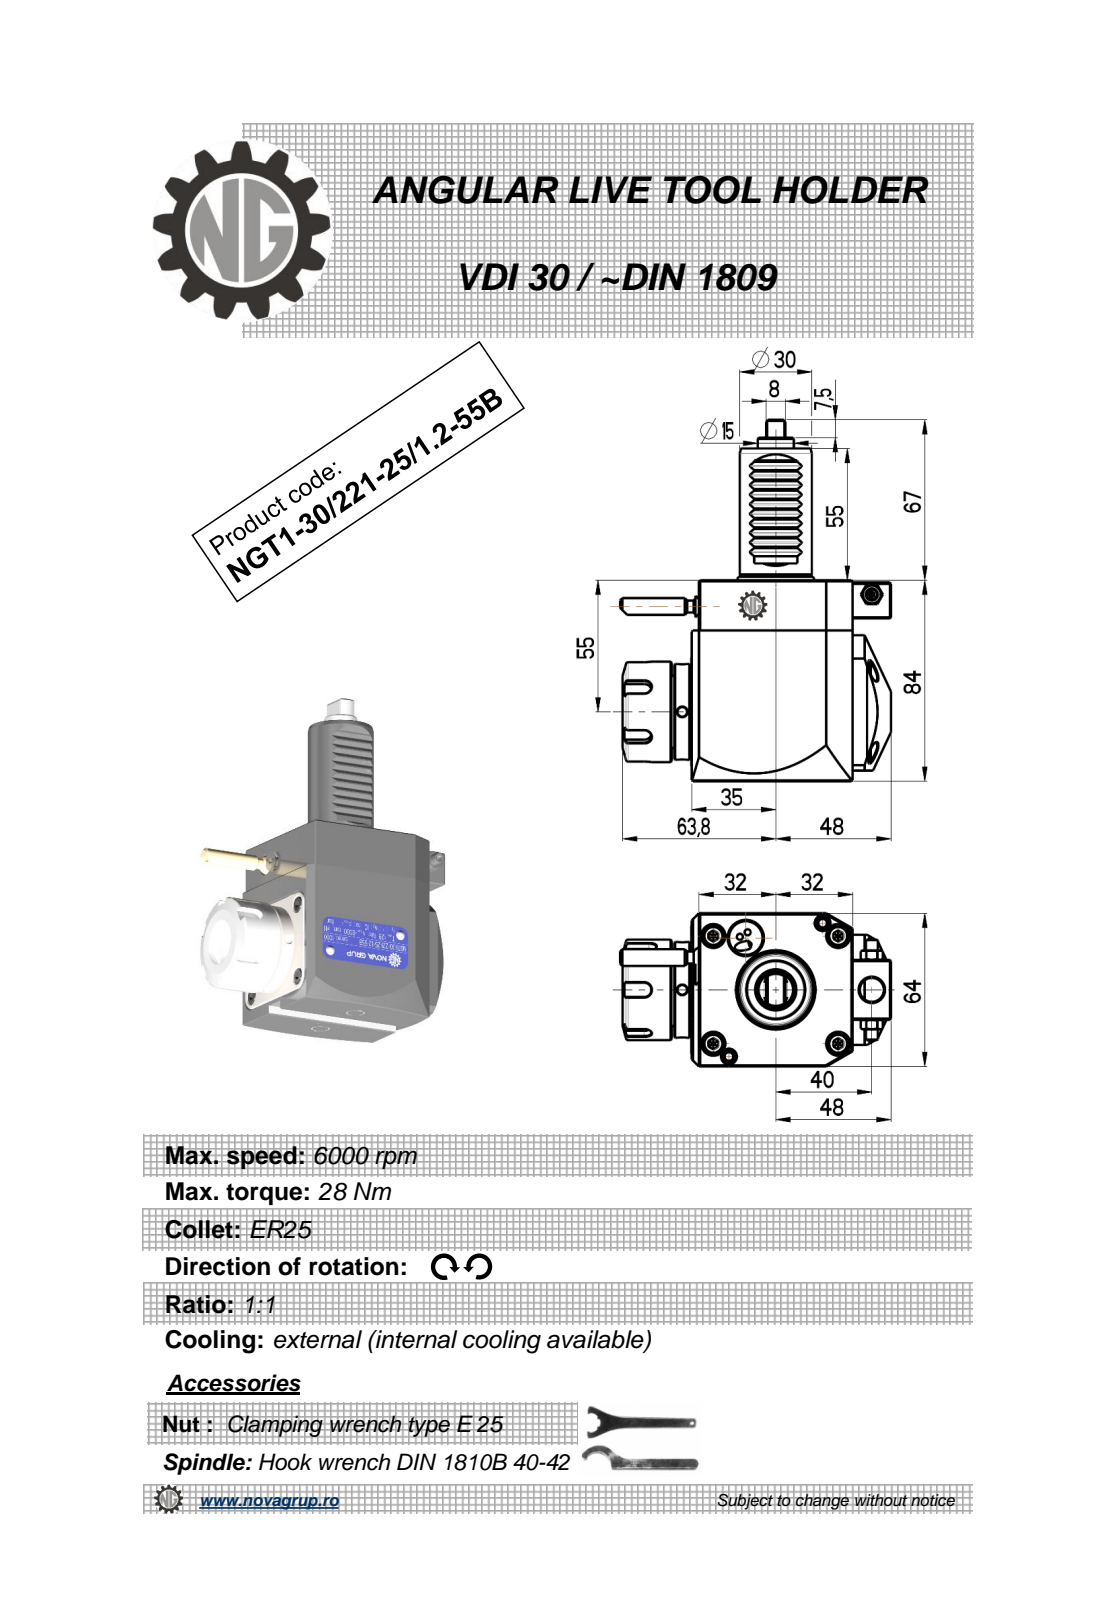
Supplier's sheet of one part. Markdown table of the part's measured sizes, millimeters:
| quantity | value |
| --- | --- |
| part name | NGT1_30_221_25_1_2_55B |
| STEP written by | PRO/ENGINEER BY PARAMETRIC TECHNOLOGY CORPORATION, 2010280 (CONFIG_CONTROL_DESIGN) |
| units | millimeters |
| bodies | 1 solid, 432 faces (194 planar, 92 cylindrical, 146 other) |
| overall size | 151 × 112.88 × 65.6 |
| volume | 451 455 mm³ |
| surface area | 46 261 mm² |
| round holes (diameter × count) | 4 × 2, 2.5 × 1, 3 × 1, 4.2 × 1, 9.5 × 1, 10 × 1, 20.3 × 1 |
| round bosses / shafts (diameter × count) | 8.96 × 2, 5 × 2, 42 × 1, 40 × 1, 33 × 1, 30 × 1, 15 × 1, 7 × 1 |
| partial cylindrical surfaces (radius × count) | 0.26 × 12, 0.3 × 10, 3 × 5, 3.5 × 4, 0.8 × 2, 160 × 2, 7.2 × 1, 32 × 1 |
| main face-to-face distances | 64, 84, 67.2, 67, 3.2, 3, 80, 83, 55, 16 |
| hole center spacings | 13.73, 46.02, 46.5, 78.95, 92.92 |
